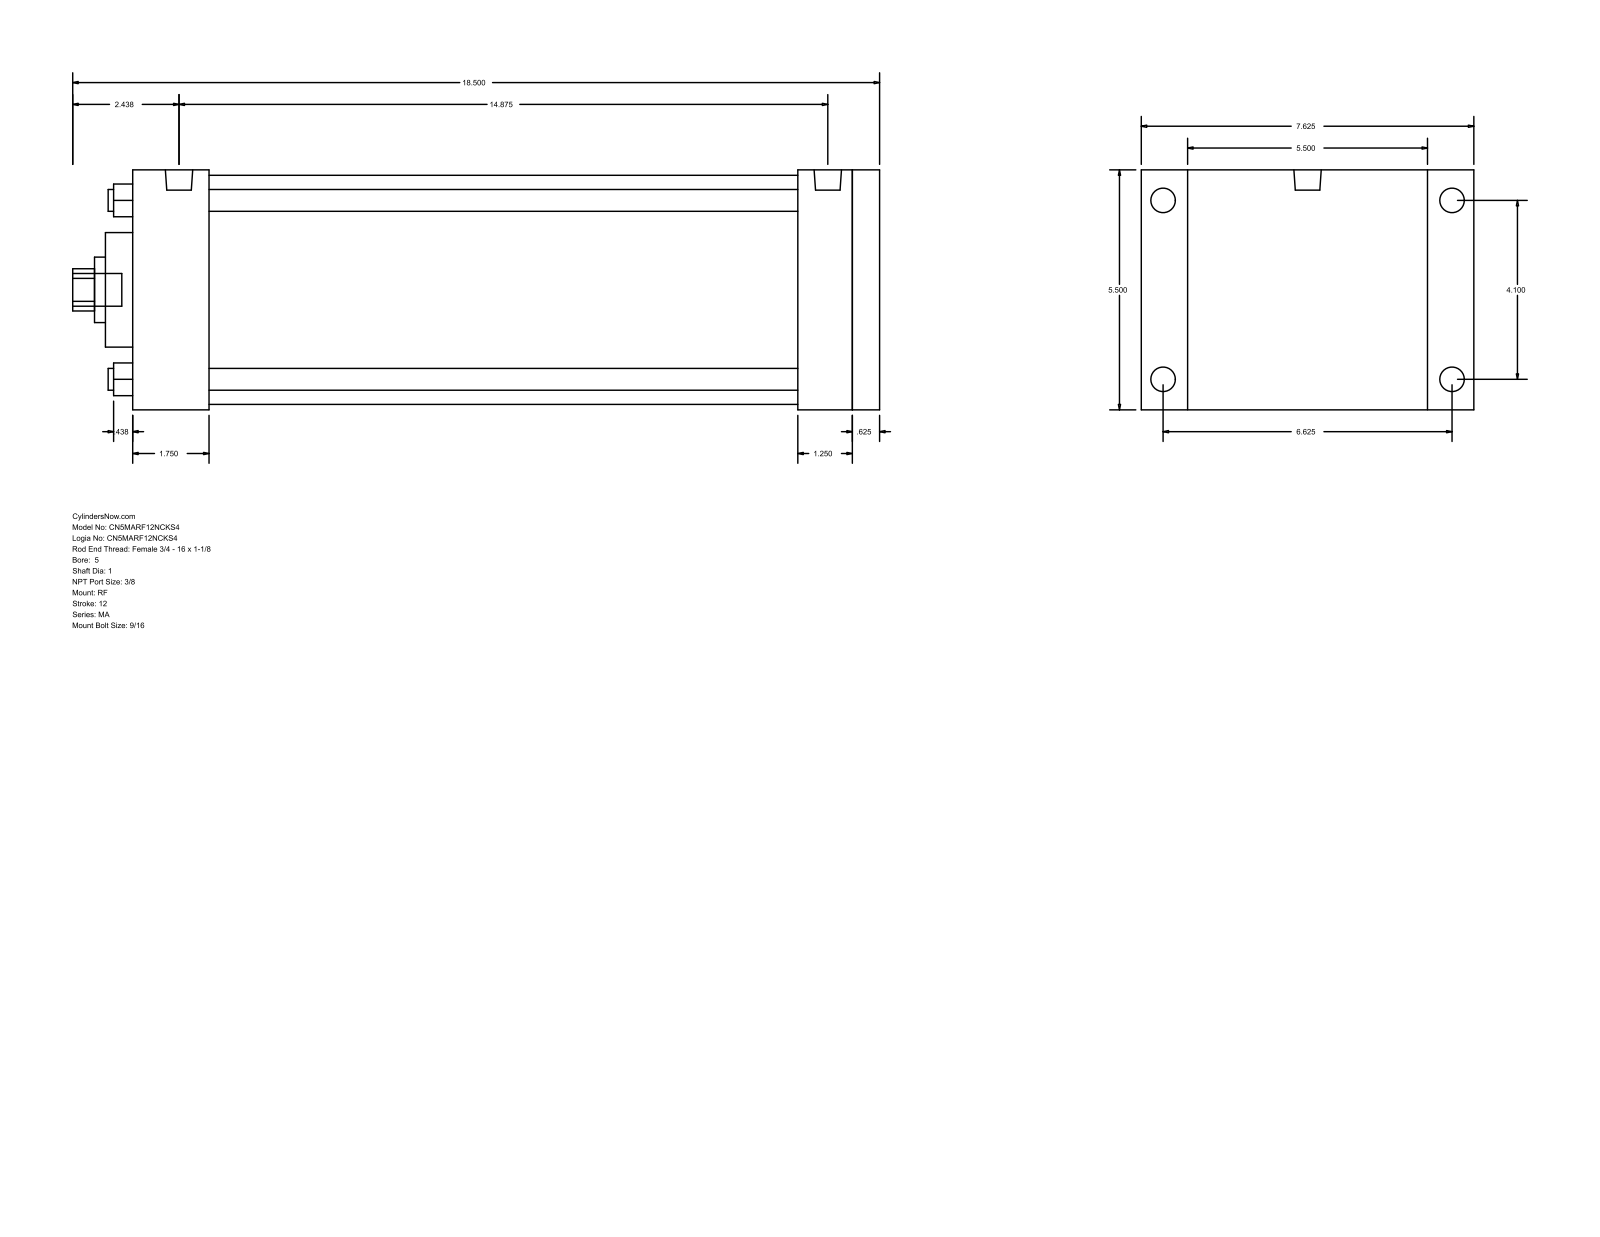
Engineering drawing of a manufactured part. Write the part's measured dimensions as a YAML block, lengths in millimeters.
part_name: "MA_RF__0500_1"
step_written_by: "GSSL Pune (CONFIG_CONTROL_DESIGN)"
units: millimeters
bodies: {solids: 0, faces: 94, planar: 65, cylindrical: 29, other: 0}
overall_size: [469.9, 193.68, 139.7]
round_holes:
  - {diameter: 12.7, count: 4}
  - {diameter: 25.4, count: 1}
  - {diameter: 38.1, count: 1}
  - {diameter: 66.67, count: 1}
  - {diameter: 133.35, count: 1}
round_bosses_or_shafts:
  - {diameter: 14.29, count: 4}
  - {diameter: 11.11, count: 4}
  - {diameter: 15.93, count: 2}
  - {diameter: 19.05, count: 1}
partial_cylinders:
  - {radius: 12.29, count: 1}
face_to_face_distances: [139.7, 434.98, 419.1, 15.88, 44.46, 374.64, 390.52, 387.35, 342.89, 31.75]
hole_center_spacings: [73.64, 104.14, 147.28]
